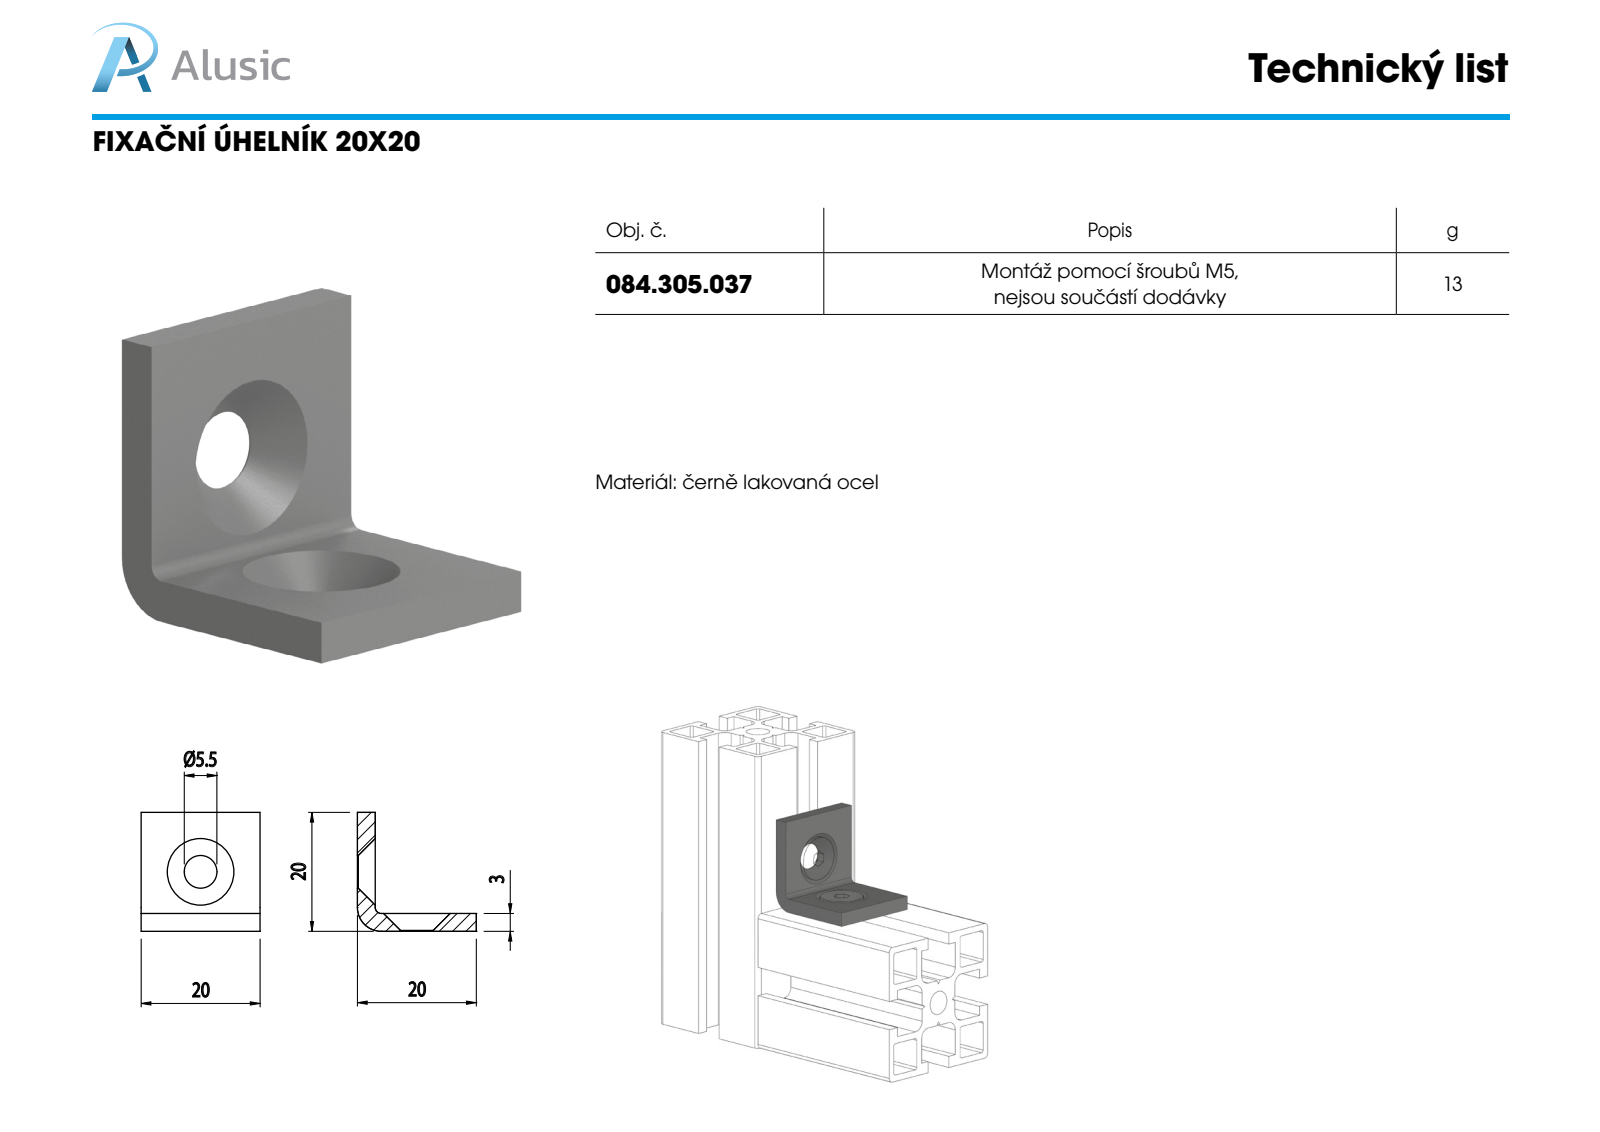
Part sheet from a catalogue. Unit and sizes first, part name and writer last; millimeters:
Units: millimetres
Overall size (bounding box): 20 × 20 × 20
Round holes (diameter × count): ⌀5.5 ×2
Main face-to-face distances: 3, 20, 17
Volume: 1 889 mm³ · Surface area: 1 794 mm²
Bodies: 1 solid, 16 faces (8 planar, 4 cylindrical, 4 other)
Part name (STEP PRODUCT): 084.305.037
STEP written by: SolidWorks 2012 (CONFIG_CONTROL_DESIGN)
